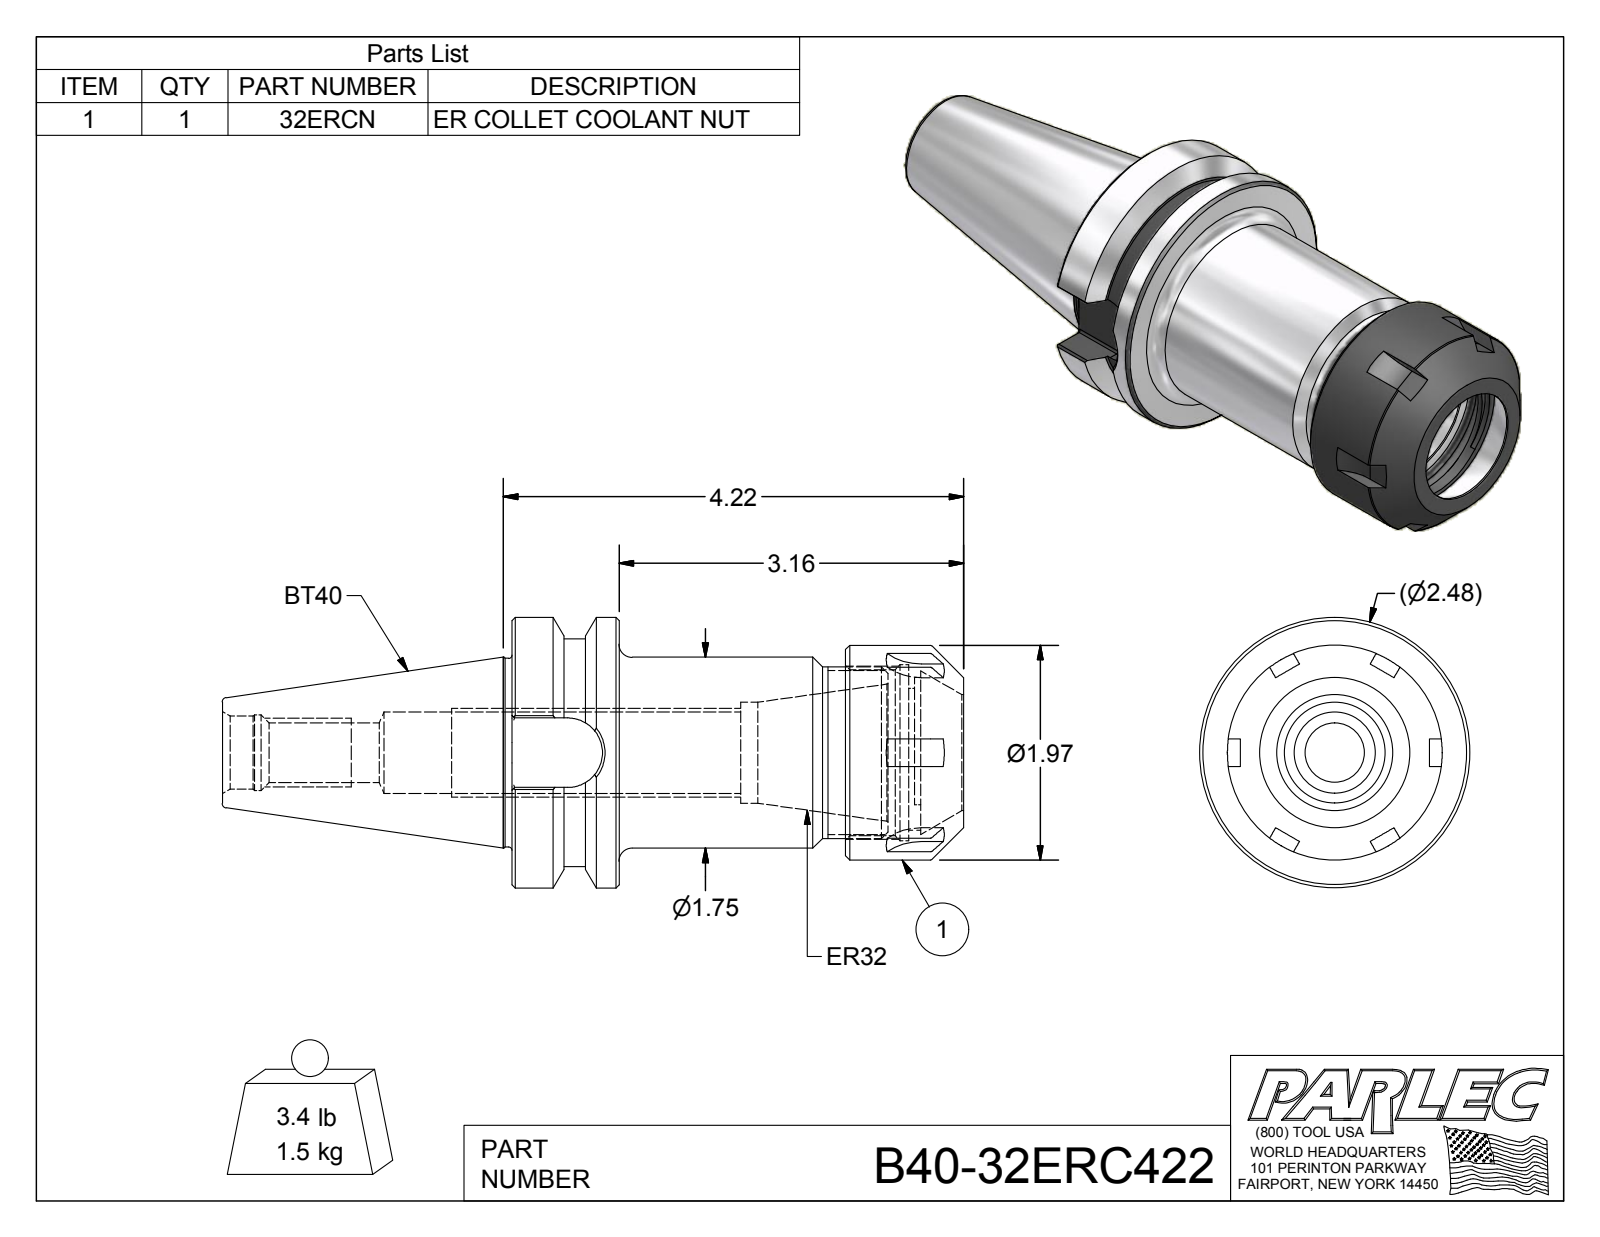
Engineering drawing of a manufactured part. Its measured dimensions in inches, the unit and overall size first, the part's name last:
Units: inches
Overall size (bounding box): 6.795 × 2.48 × 2.48
Round holes (diameter × count): ⌀0.545 ×1, ⌀0.67 ×1, ⌀0.694 ×1, ⌀0.745 ×1, ⌀0.925 ×1, ⌀1.063 ×1, ⌀1.299 ×1, ⌀1.522 ×1, ⌀1.614 ×1
Round bosses / shafts (diameter × count): ⌀2.48 ×1, ⌀2.087 ×1, ⌀1.969 ×1, ⌀1.75 ×1, ⌀1.73 ×1, ⌀1.575 ×1
Partial cylindrical surfaces — rounded edges, fillets, slot ends (radius × count): R0.02 ×8, R0.5 ×6, R0.319 ×1, R0.689 ×1
Main face-to-face distances: 0.984, 3.059, 2.076, 3.638, 2.654, 0.579, 4.142, 3.158, 1.083, 0.504
Hole centre spacings: 0.059
Volume: 11.89 in³ · Surface area: 69.95 in²
Bodies: 2 solids, 117 faces (47 planar, 35 cylindrical, 35 other)
Part name (STEP PRODUCT): B40-32ERC422; B40-32ER4-1; 32ERCN
STEP written by: Autodesk Inventor 2012 (AUTOMOTIVE_DESIGN)
